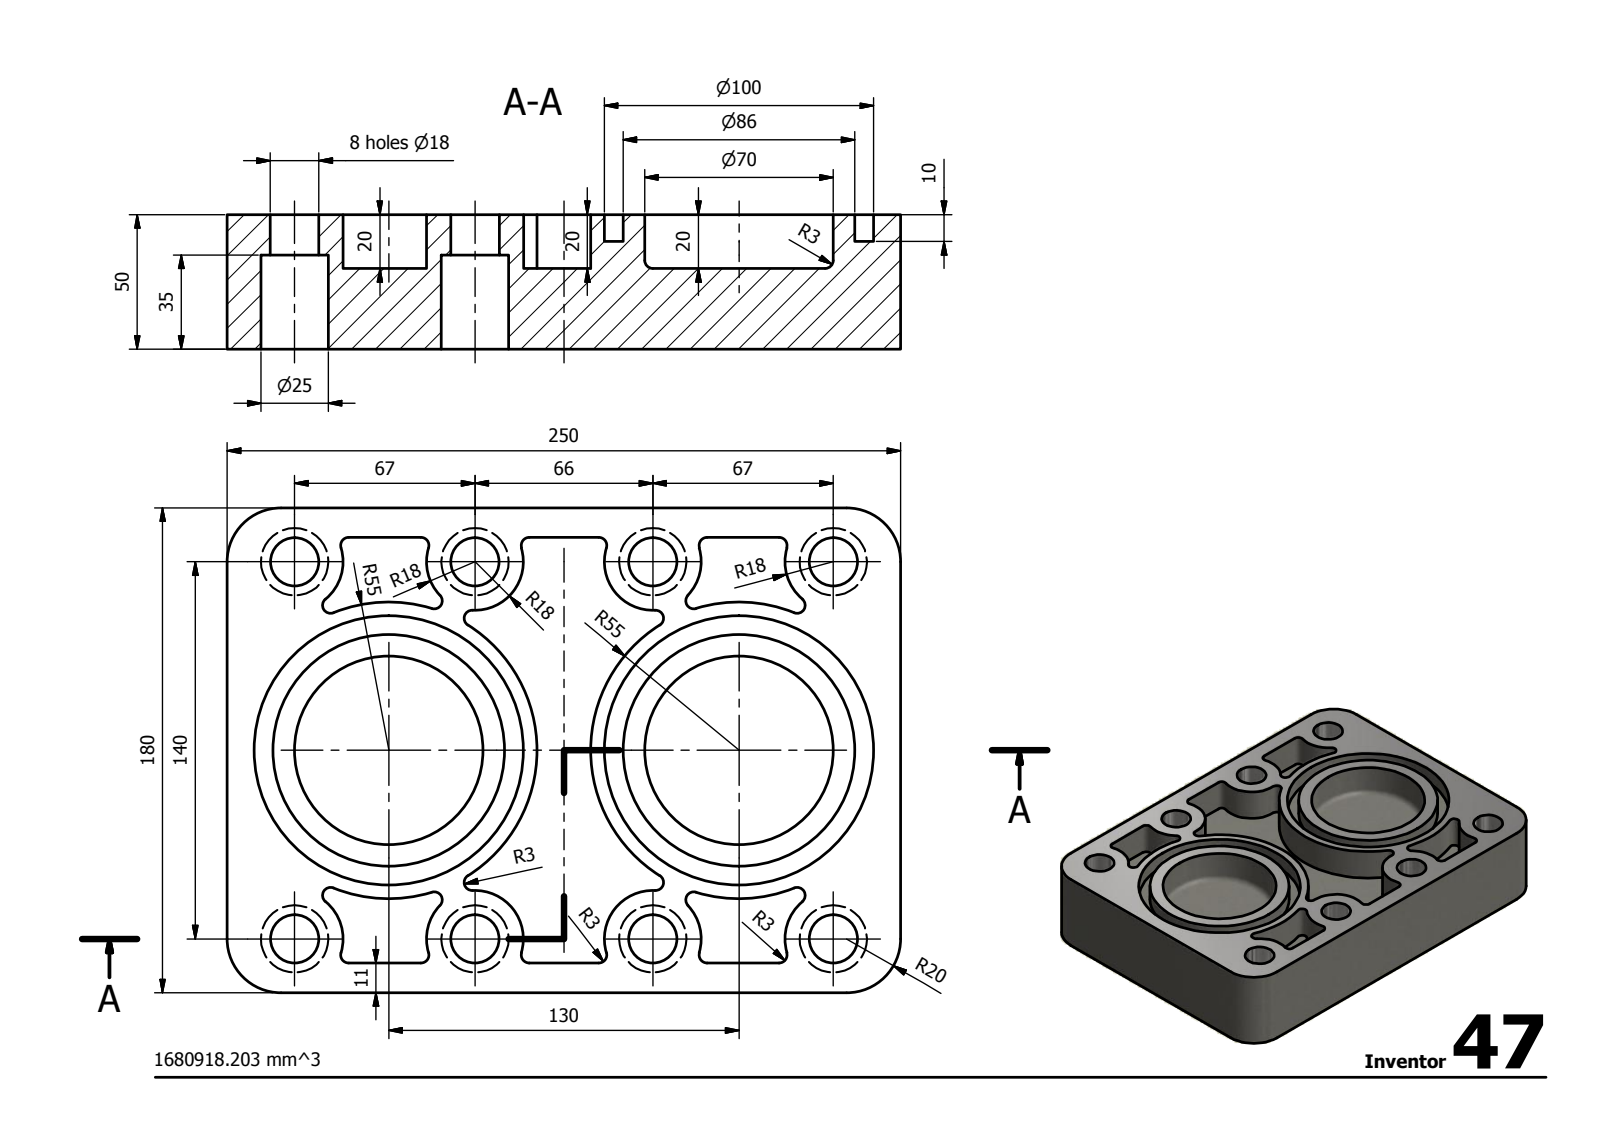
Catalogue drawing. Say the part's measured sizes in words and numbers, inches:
Its 3-D file was written by "Autodesk Inventor 2014 (AUTOMOTIVE_DESIGN)". It is 1 solid with 101 faces: 31 planar, 68 cylindrical and 2 other. Overall it measures 9.843 by 7.087 by 1.969 inches. Its volume is 102.6 cubic inches and its surface area 302.3 square inches. Round holes: 8 of diameter 0.709, 8 of diameter 0.984, 2 of diameter 2.756, 2 of diameter 3.937. Round bosses or shafts: 2 of diameter 3.386. Partial cylindrical surfaces (rounded edges, fillets, slot ends): 24 of radius 0.118, 8 of radius 0.709, 4 of radius 0.787, 2 of radius 2.165. The main face-to-face distances are 1.969, 1.181, 0.787, 7.087, 0.394, 9.843, 1.575, 0.197, 0.433, 6.654. The hole center spacings are 2.638, 3.03, 3.081, 4.741, 5.236, 5.512, 6.111, 7.056.
